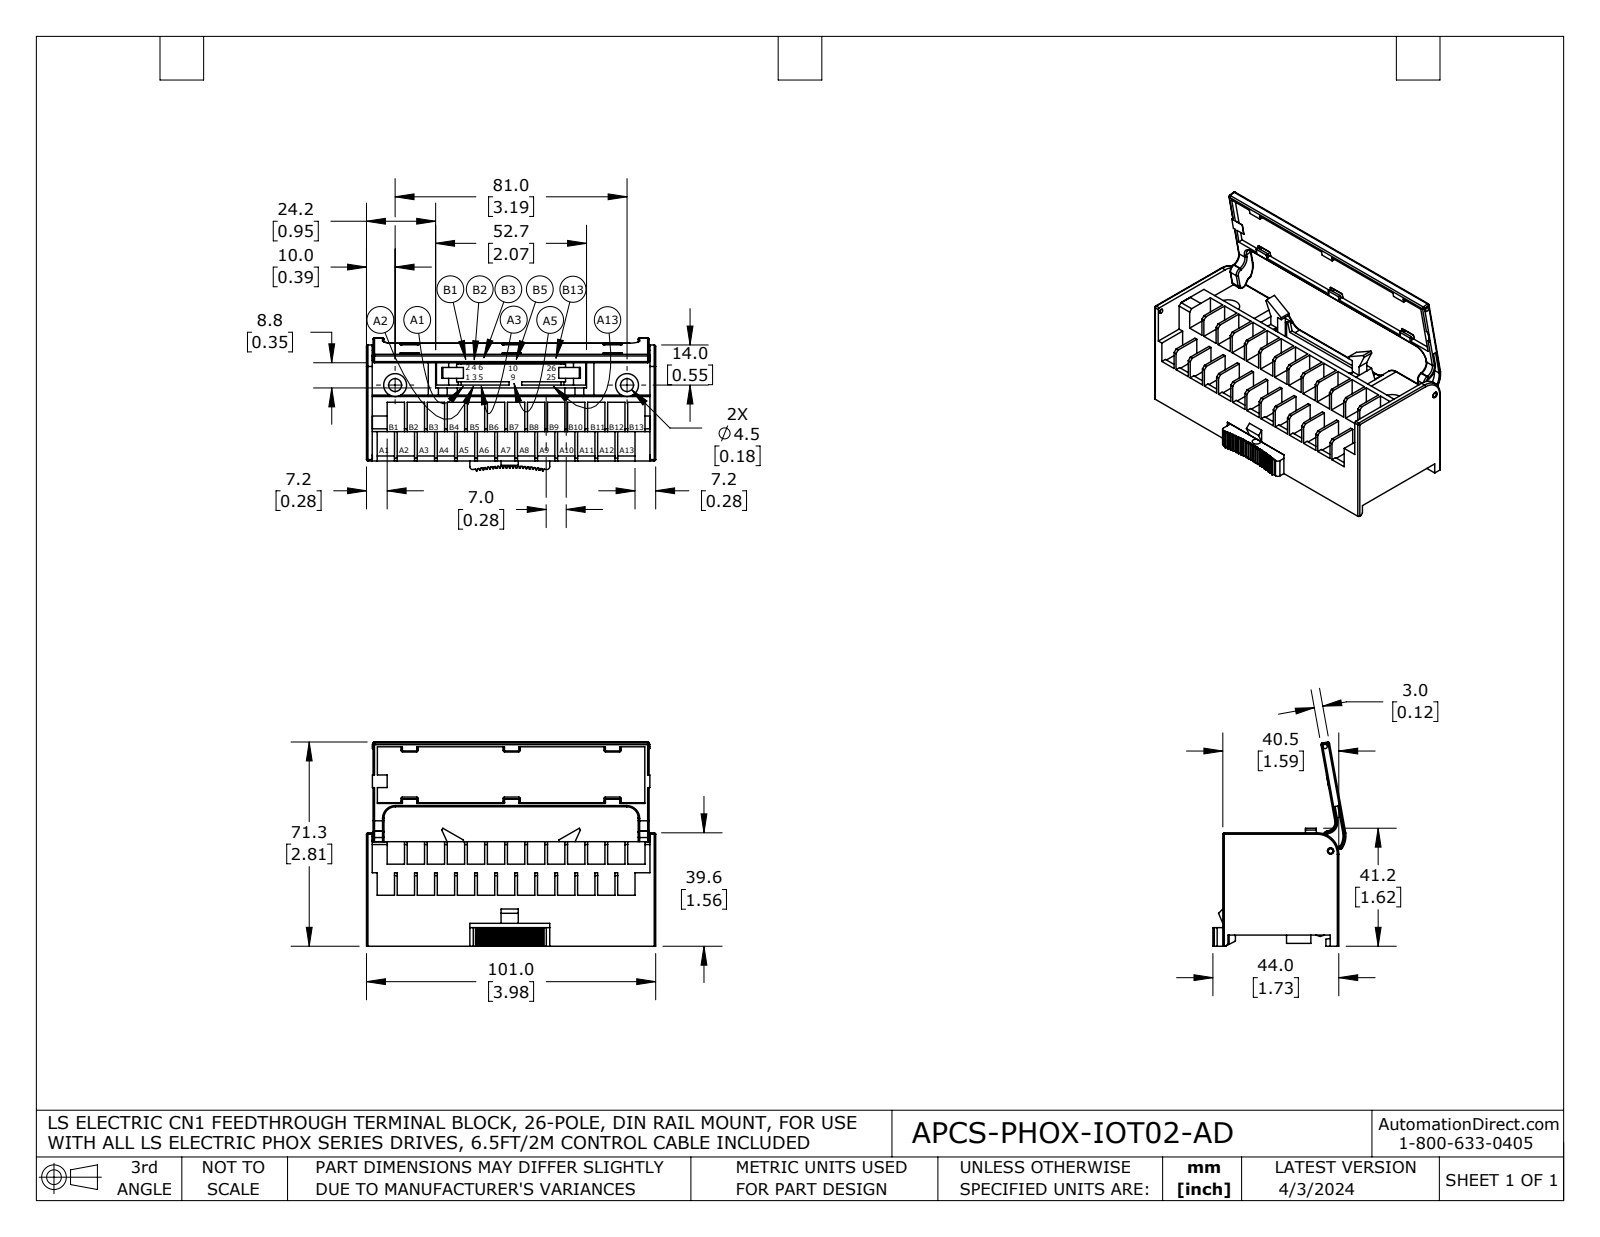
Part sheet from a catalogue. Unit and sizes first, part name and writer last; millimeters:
Units: millimetres
Overall size (bounding box): 101 × 44 × 41.2
Round holes (diameter × count): ⌀4.5 ×2, ⌀8 ×2, ⌀2.2 ×1, ⌀3 ×1
Round bosses / shafts (diameter × count): ⌀8.5 ×2, ⌀2 ×1, ⌀1.5 ×1
Partial cylindrical surfaces — rounded edges, fillets, slot ends (radius × count): R0.5 ×67, R4 ×5, R1 ×4, R2 ×4, R5 ×4, R0.3 ×2, R0.4 ×2, R5.5 ×2
Main face-to-face distances: 1.5, 10.3, 40.5, 101, 14, 2, 24.7, 40.3, 3, 30.3
Hole centre spacings: 47.8, 48.6, 81
Volume: 99 720 mm³ · Surface area: 34 600 mm²
Bodies: 2 solids, 694 faces (458 planar, 175 cylindrical, 61 other)
Part name (STEP PRODUCT): APCS-PHOX-IOT02-AD
STEP written by: SolidWorks 2021 (AUTOMOTIVE_DESIGN)
